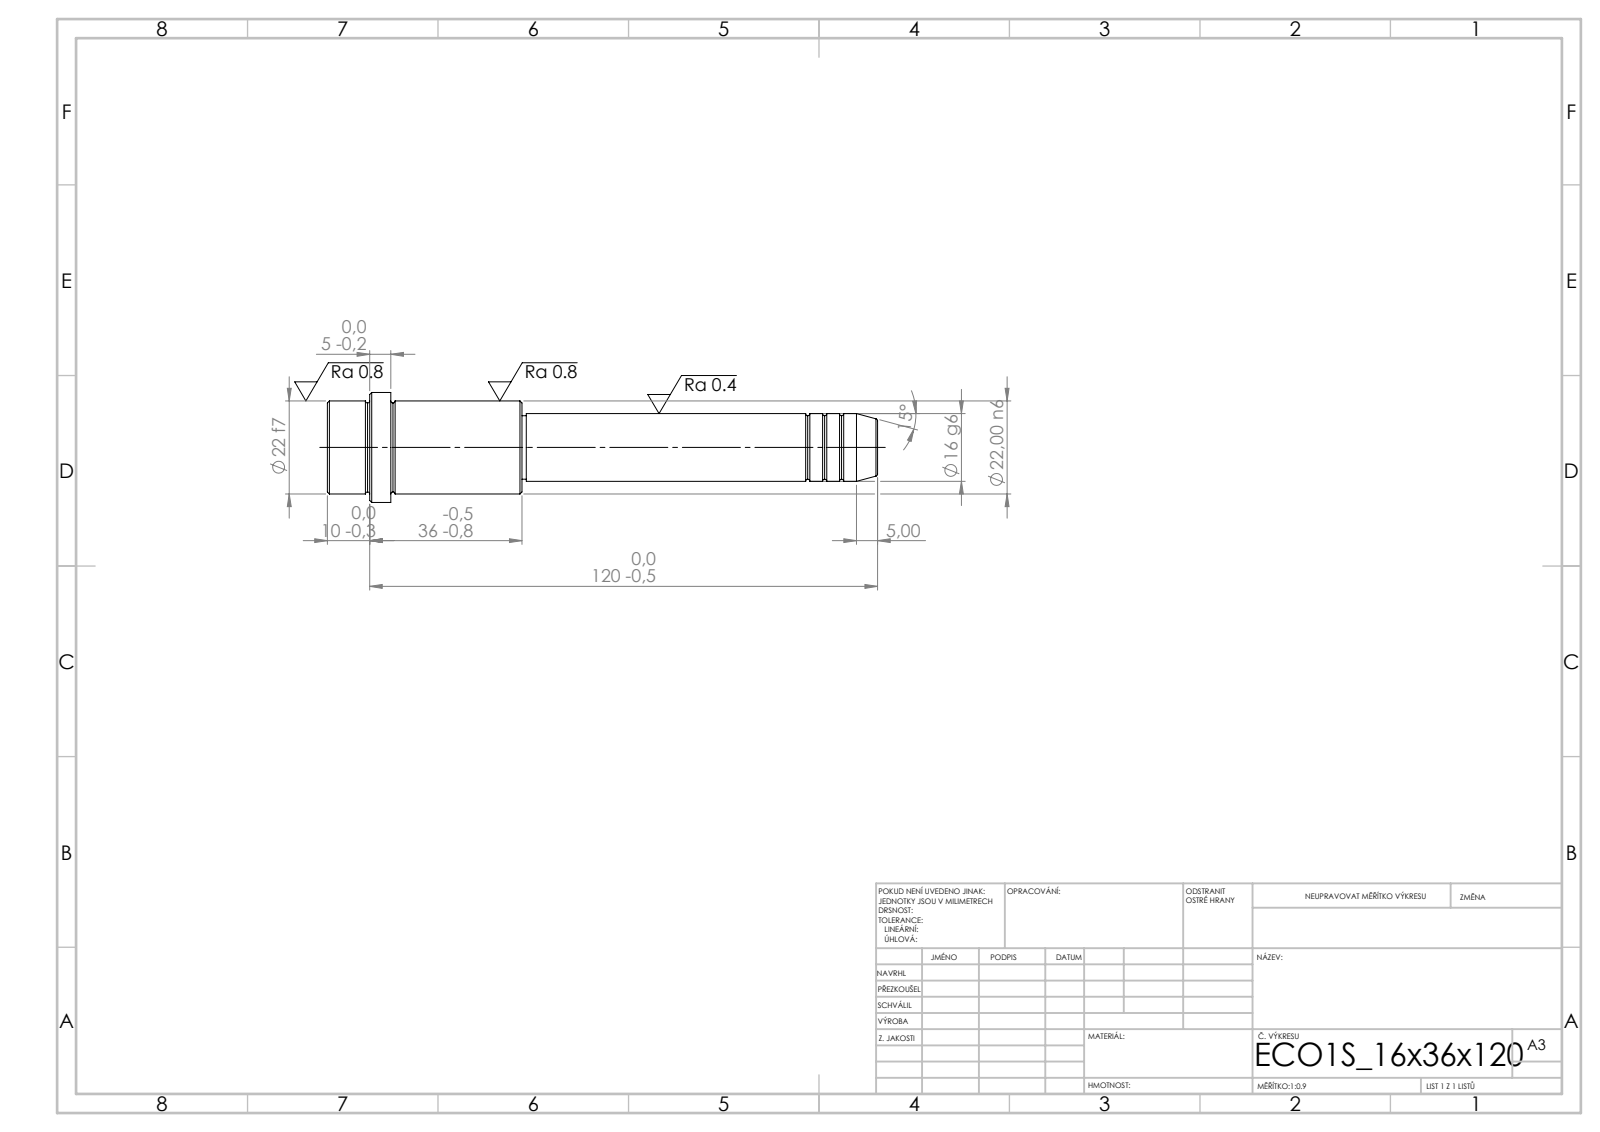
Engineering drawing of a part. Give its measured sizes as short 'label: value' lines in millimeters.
written by: SolidWorks 2019 (CONFIG_CONTROL_DESIGN)
unit: mm
bodies: 1 solid, 52 faces (6 planar, 16 cylindrical, 30 other)
size: 130 × 26 × 26
volume: 34 807 mm³; area: 8 576 mm²
bosses: 1× ⌀26, 1× ⌀22, 1× ⌀16, 1× ⌀15
face distances: 46, 31, 15, 84, 115, 130, 120, 36, 5, 10
